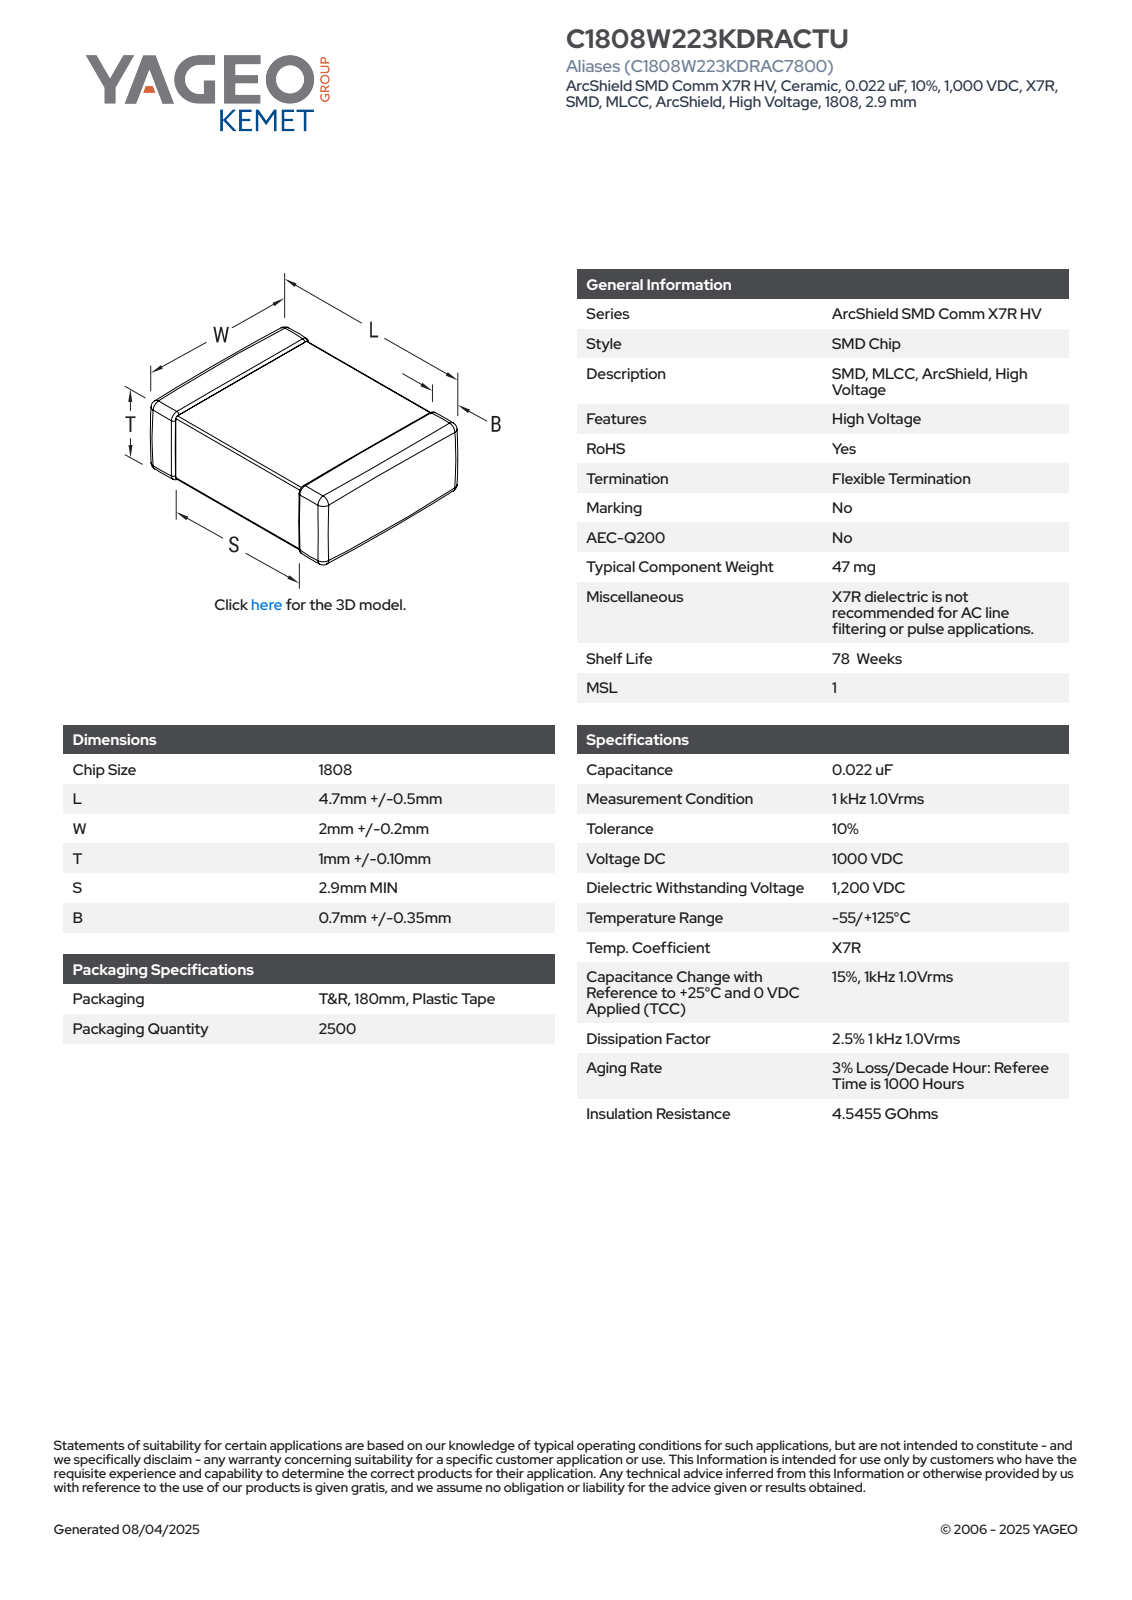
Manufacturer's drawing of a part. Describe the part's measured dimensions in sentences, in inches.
The part is named "CCS_CCSTD_1808_L5.2W2.2T1.1B0.7". Its 3-D file was written by "SolidWorks 2021 (AUTOMOTIVE_DESIGN)". It is 4 solids with 129 faces: 71 planar, 42 cylindrical and 16 other. Overall it measures 0.205 by 0.087 by 0.043 inches. Its volume is 0.001 cubic inches and its surface area 0.059 square inches. The main face-to-face distances are 0.041, 0.039, 0.043, 0.085, 0.083, 0.205, 0.087, 0.042, 0.04, 0.013.
